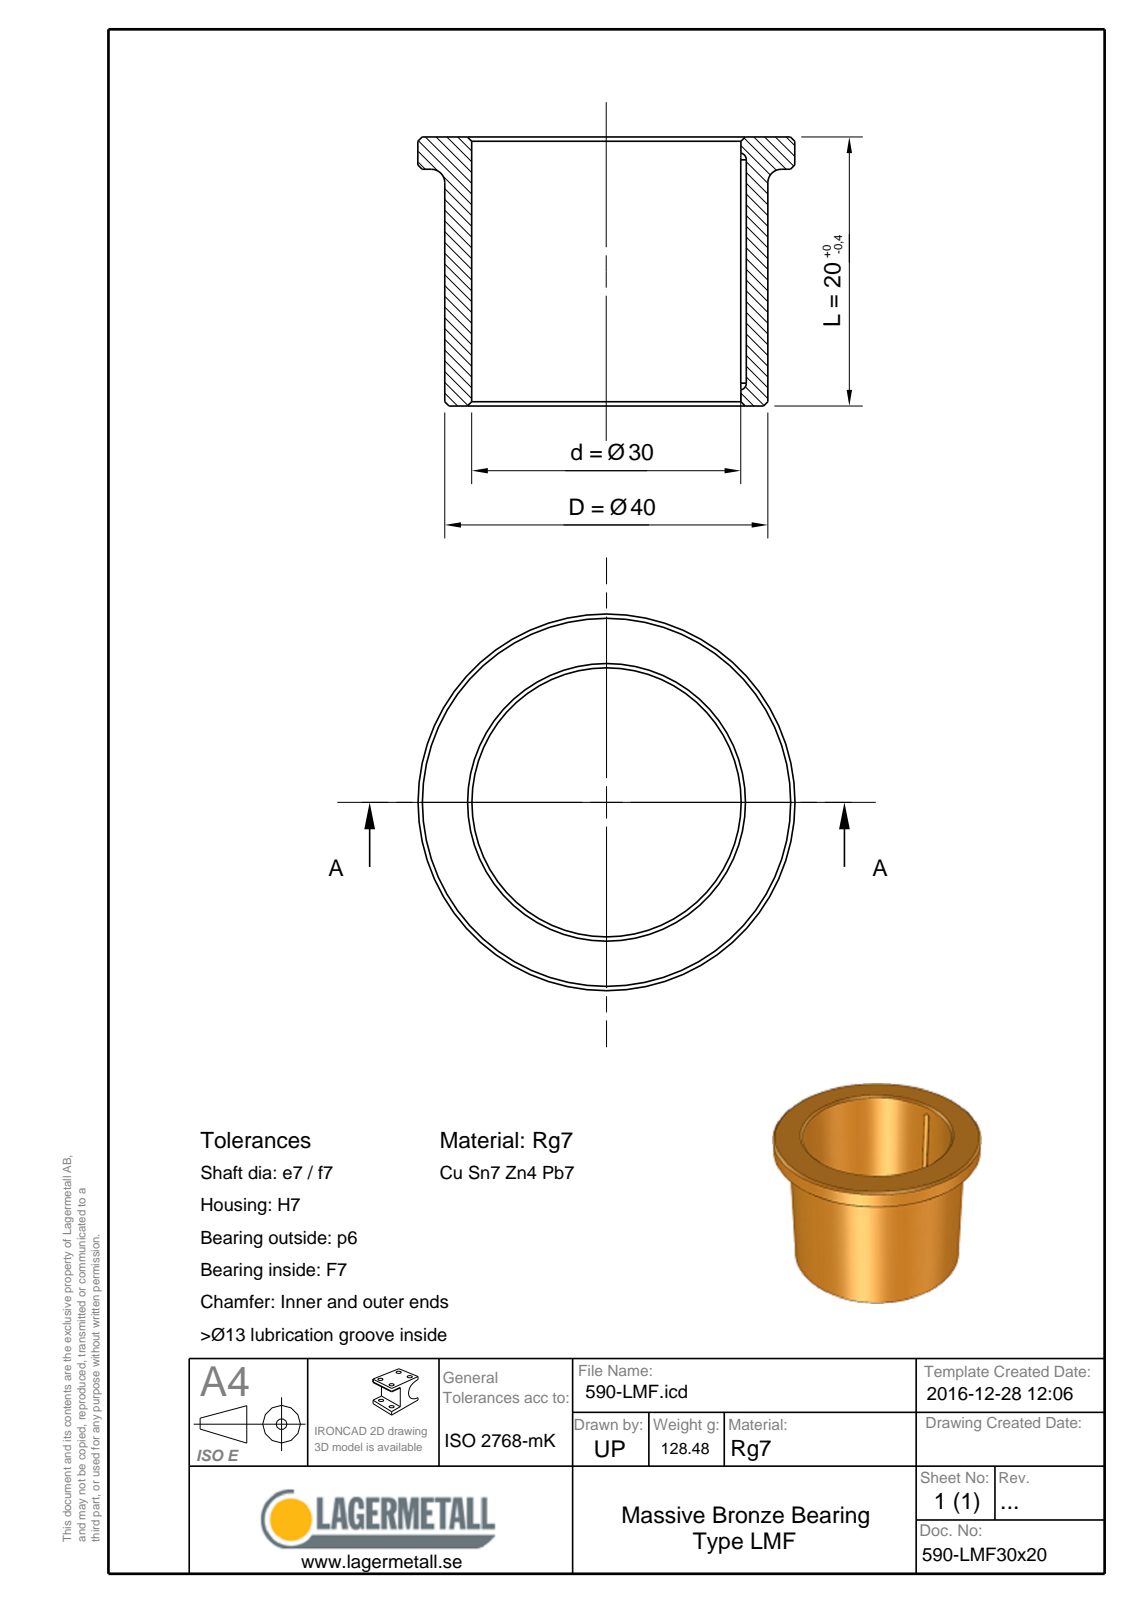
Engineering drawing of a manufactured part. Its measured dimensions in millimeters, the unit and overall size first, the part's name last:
Units: millimetres
Overall size (bounding box): 50 × 50 × 20
Round holes (diameter × count): ⌀30 ×1
Round bosses / shafts (diameter × count): ⌀50 ×1, ⌀40 ×1
Partial cylindrical surfaces — rounded edges, fillets, slot ends (radius × count): R1.25 ×2
Main face-to-face distances: 20, 15, 5
Volume: 14 602 mm³ · Surface area: 6 767 mm²
Bodies: 1 solid, 17 faces (4 planar, 5 cylindrical, 8 other)
Part name (STEP PRODUCT): 590-LMF30x20
STEP written by: Spatial InterOp 3D (CONFIG_CONTROL_DESIGN)
